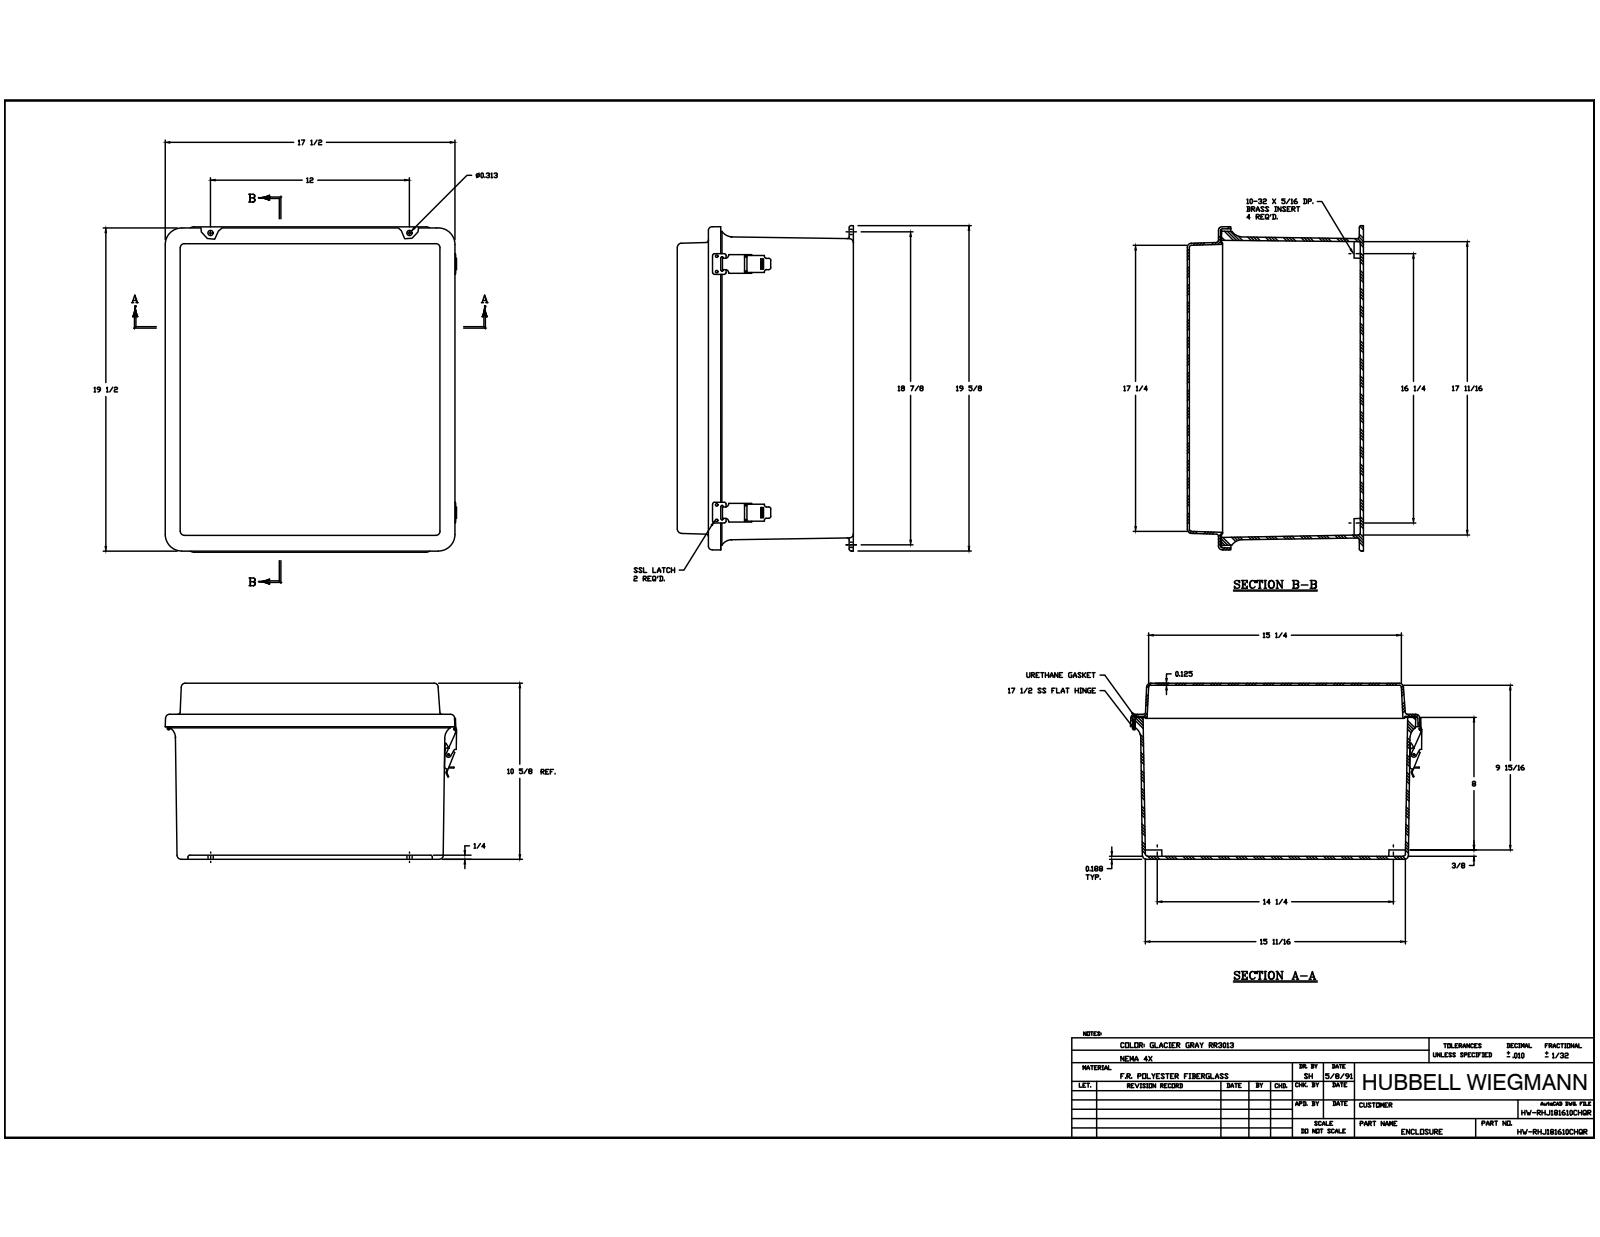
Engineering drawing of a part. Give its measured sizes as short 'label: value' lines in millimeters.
name: J1816HL_6; RMINS45821P_155; RMINS45821P_156; RMINS45821P_157 (+8 more)
written by: Autodesk Inventor 2014 (AUTOMOTIVE_DESIGN)
unit: mm
bodies: 42 solids, 1200 faces (530 planar, 495 cylindrical, 175 other)
size: 498.48 × 447.77 × 270.3
volume: 4 091 000 mm³; area: 1 903 000 mm²
holes: 24× ⌀3.56, 12× ⌀3.33, 8× ⌀2.64, 5× ⌀3.86, 4× ⌀3.3, 4× ⌀3.96, 4× ⌀5.54, 2× ⌀3.43, 2× ⌀9.52, 1× ⌀2.16, 1× ⌀2.16
bosses: 20× ⌀3.17, 12× ⌀6.35, 4× ⌀6.86, 1× ⌀7.62, 1× ⌀4.31, 1× ⌀3.94, 1× ⌀3.05
rounds: 28× R3.17, 20× R0.38, 20× R0.79, 16× R1.14, 12× R0.76, 12× R6.35, 9× R0.57, 6× R1.52
face distances: 4.76, 4.77, 3.18, 267.13, 262.36, 270.31, 265.54, 50.8, 3.17, 219.51
hole spacings: 85.72, 85.73, 171.45, 6.35, 260.35, 380.59, 247.65, 254
